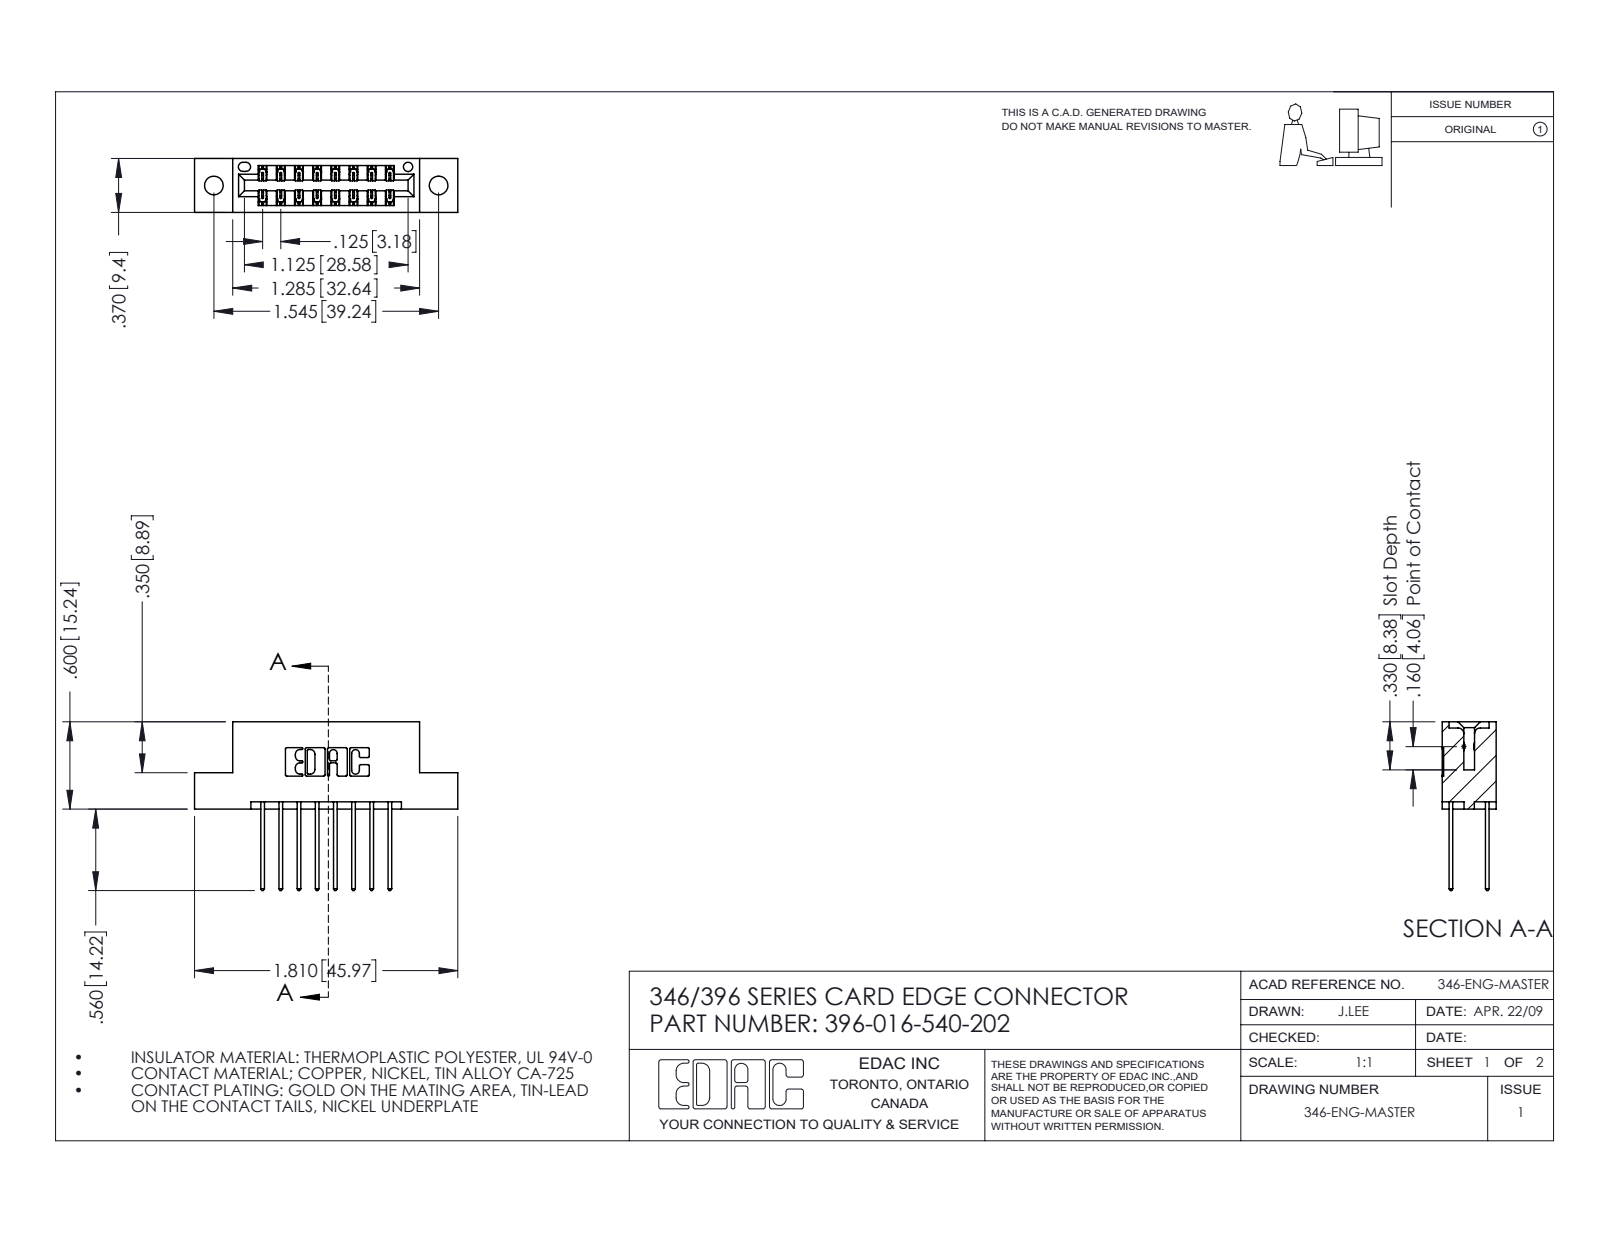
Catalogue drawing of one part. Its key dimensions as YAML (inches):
part_name: "346 Part_Flush Mounting Lugs - 0.128 Dia; 396-016-540-202; 345-292-001_345-293-140"
step_written_by: "SolidWorks 2016 (CONFIG_CONTROL_DESIGN)"
units: inches
bodies: {solids: 17, faces: 954, planar: 636, cylindrical: 318, other: 0}
overall_size: [1.81, 1.16, 0.37]
volume: 0.259
surface_area: 8.239
round_holes:
  - {diameter: 0.128, count: 2}
  - {diameter: 0.064, count: 1}
partial_cylinders:
  - {radius: 0.006, count: 24}
  - {radius: 0.01, count: 22}
  - {radius: 0.01, count: 16}
  - {radius: 0.007, count: 6}
  - {radius: 0.031, count: 6}
  - {radius: 0.026, count: 3}
  - {radius: 0.014, count: 2}
  - {radius: 0.022, count: 2}
face_to_face_distances: [0.25, 0.048, 0.322, 0.37, 0.072, 0.298, 0.025, 0.275, 0.5, 0.148]
hole_center_spacings: [0.246, 1.341, 1.545]
